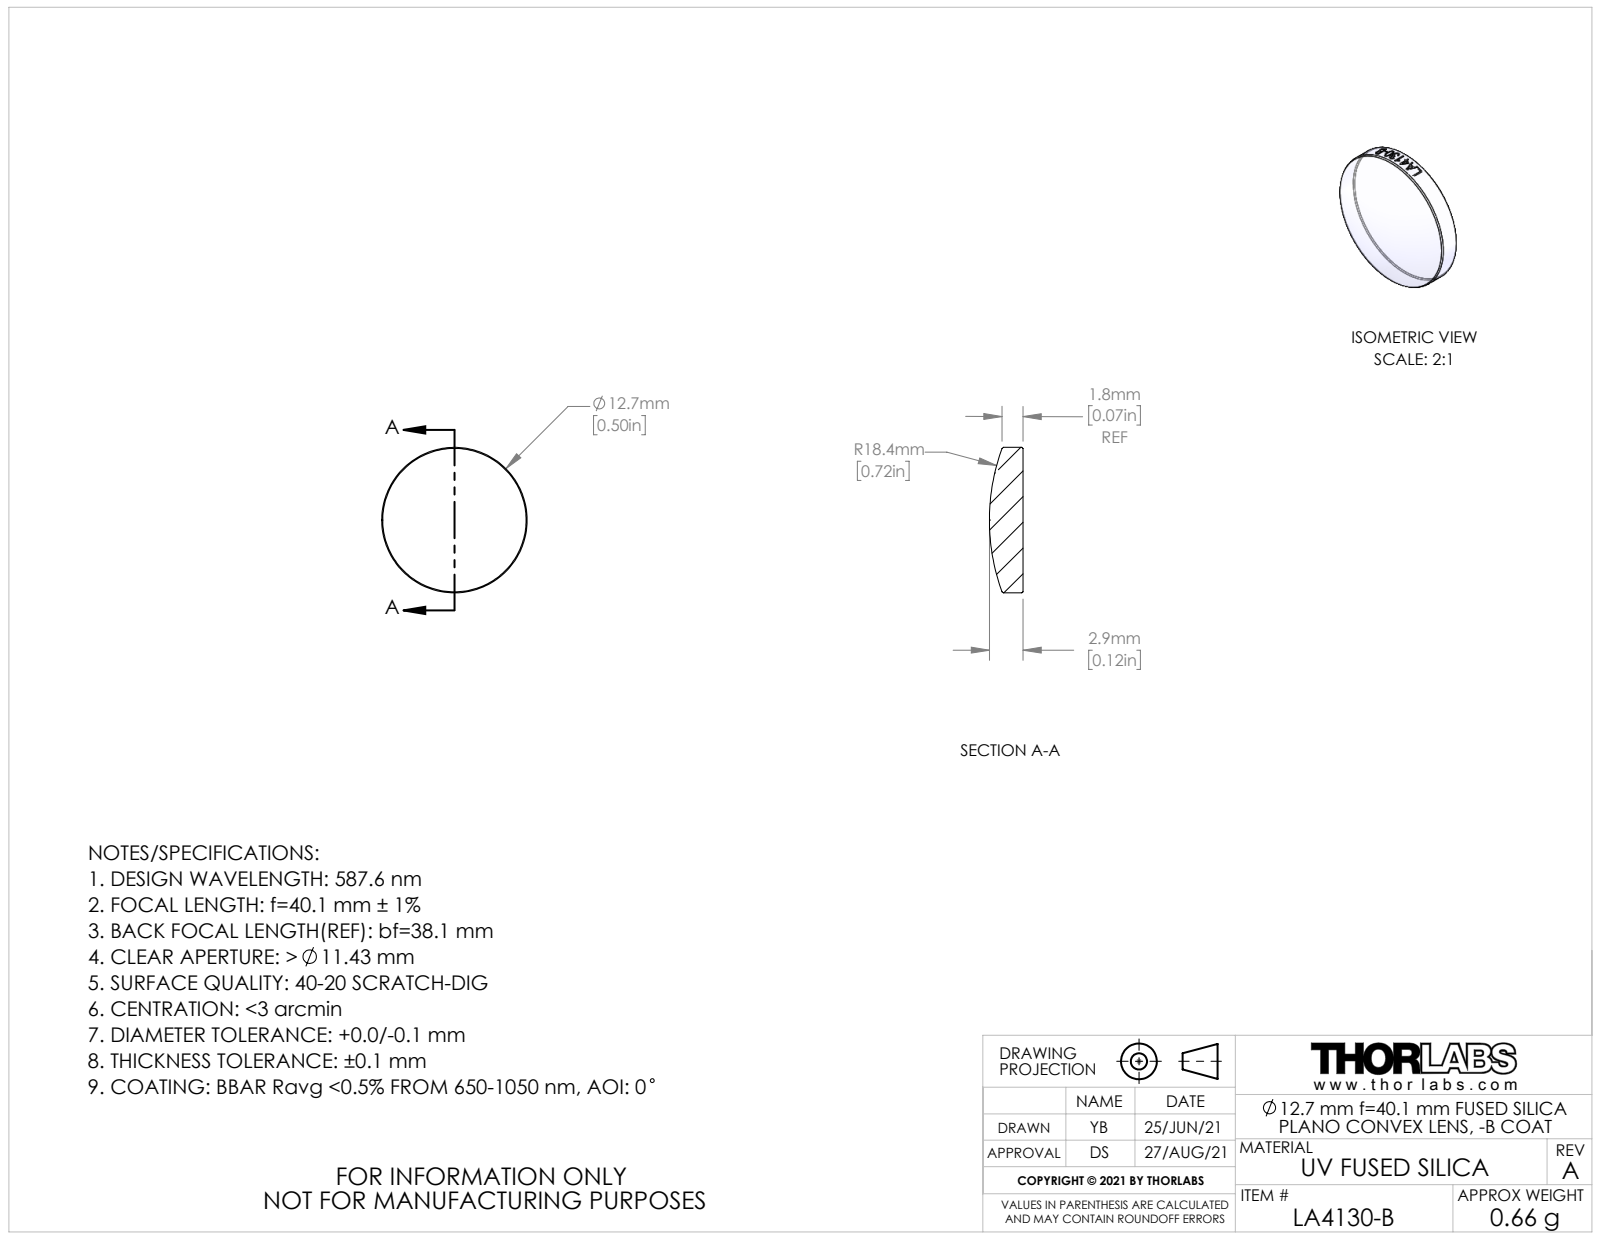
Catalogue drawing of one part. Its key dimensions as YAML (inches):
part_name: "CTN017895-E0W"
step_written_by: "SolidWorks 2018 (AUTOMOTIVE_DESIGN)"
units: inches
bodies: {solids: 1, faces: 22, planar: 1, cylindrical: 15, other: 6}
overall_size: [0.5, 0.5, 0.115]
volume: 0.018
surface_area: 0.504
round_bosses_or_shafts:
  - {diameter: 0.5, count: 1}
